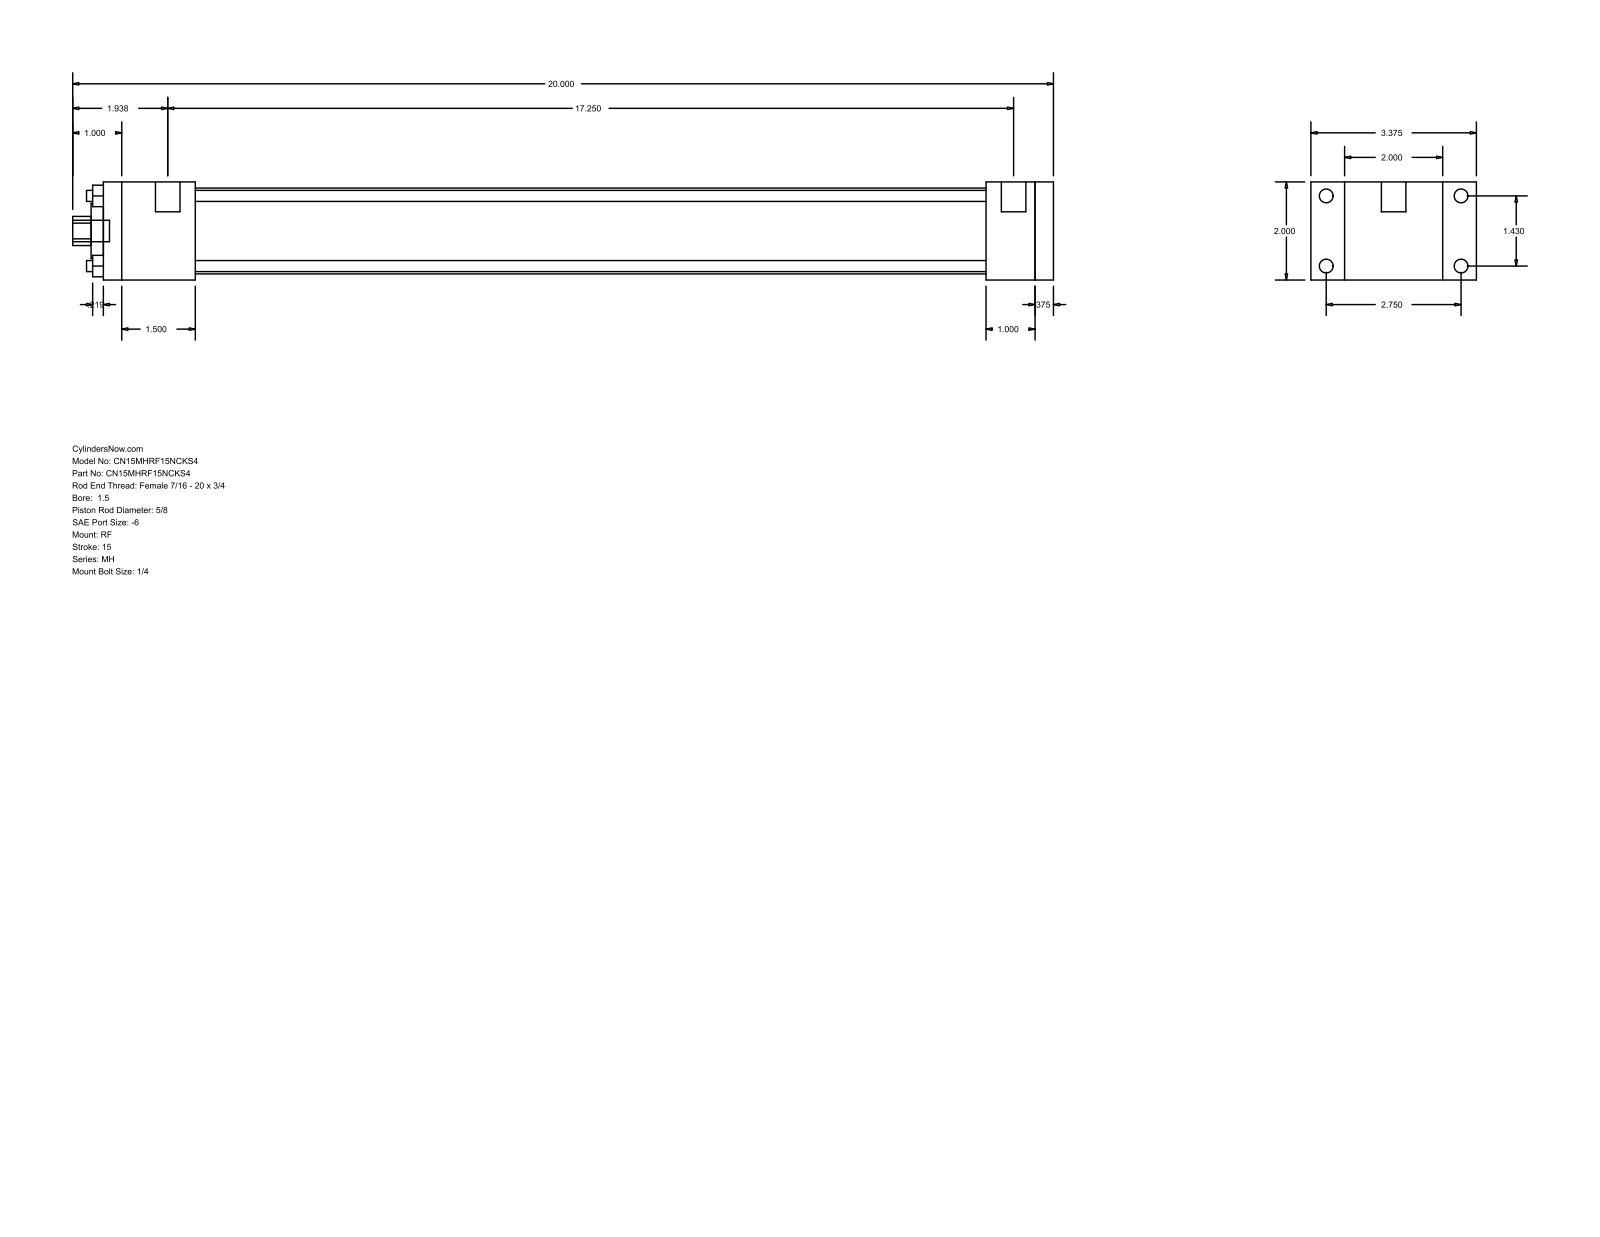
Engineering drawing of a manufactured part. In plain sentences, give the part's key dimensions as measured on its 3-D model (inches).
The part is named "MH_RF__0150_0.625". Its 3-D file was written by "GSSL Pune (CONFIG_CONTROL_DESIGN)". It is 0 solids with 92 faces: 64 planar, 28 cylindrical and 0 other. Overall it measures 20 by 3.375 by 2 inches. Round holes: 4 of diameter 0.225, 1 of diameter 0.625, 1 of diameter 1.125, 1 of diameter 1.75. Round bosses or shafts: 4 of diameter 0.281, 4 of diameter 0.219, 2 of diameter 0.5, 1 of diameter 0.437. Partial cylindrical surfaces (rounded edges, fillets, slot ends): 1 of radius 0.297. The main face-to-face distances are 2, 0.375, 19, 19.375, 0.687, 2.687, 18, 1, 1.375, 1.875. The hole center spacings are 1.011, 1.43, 2.022.
